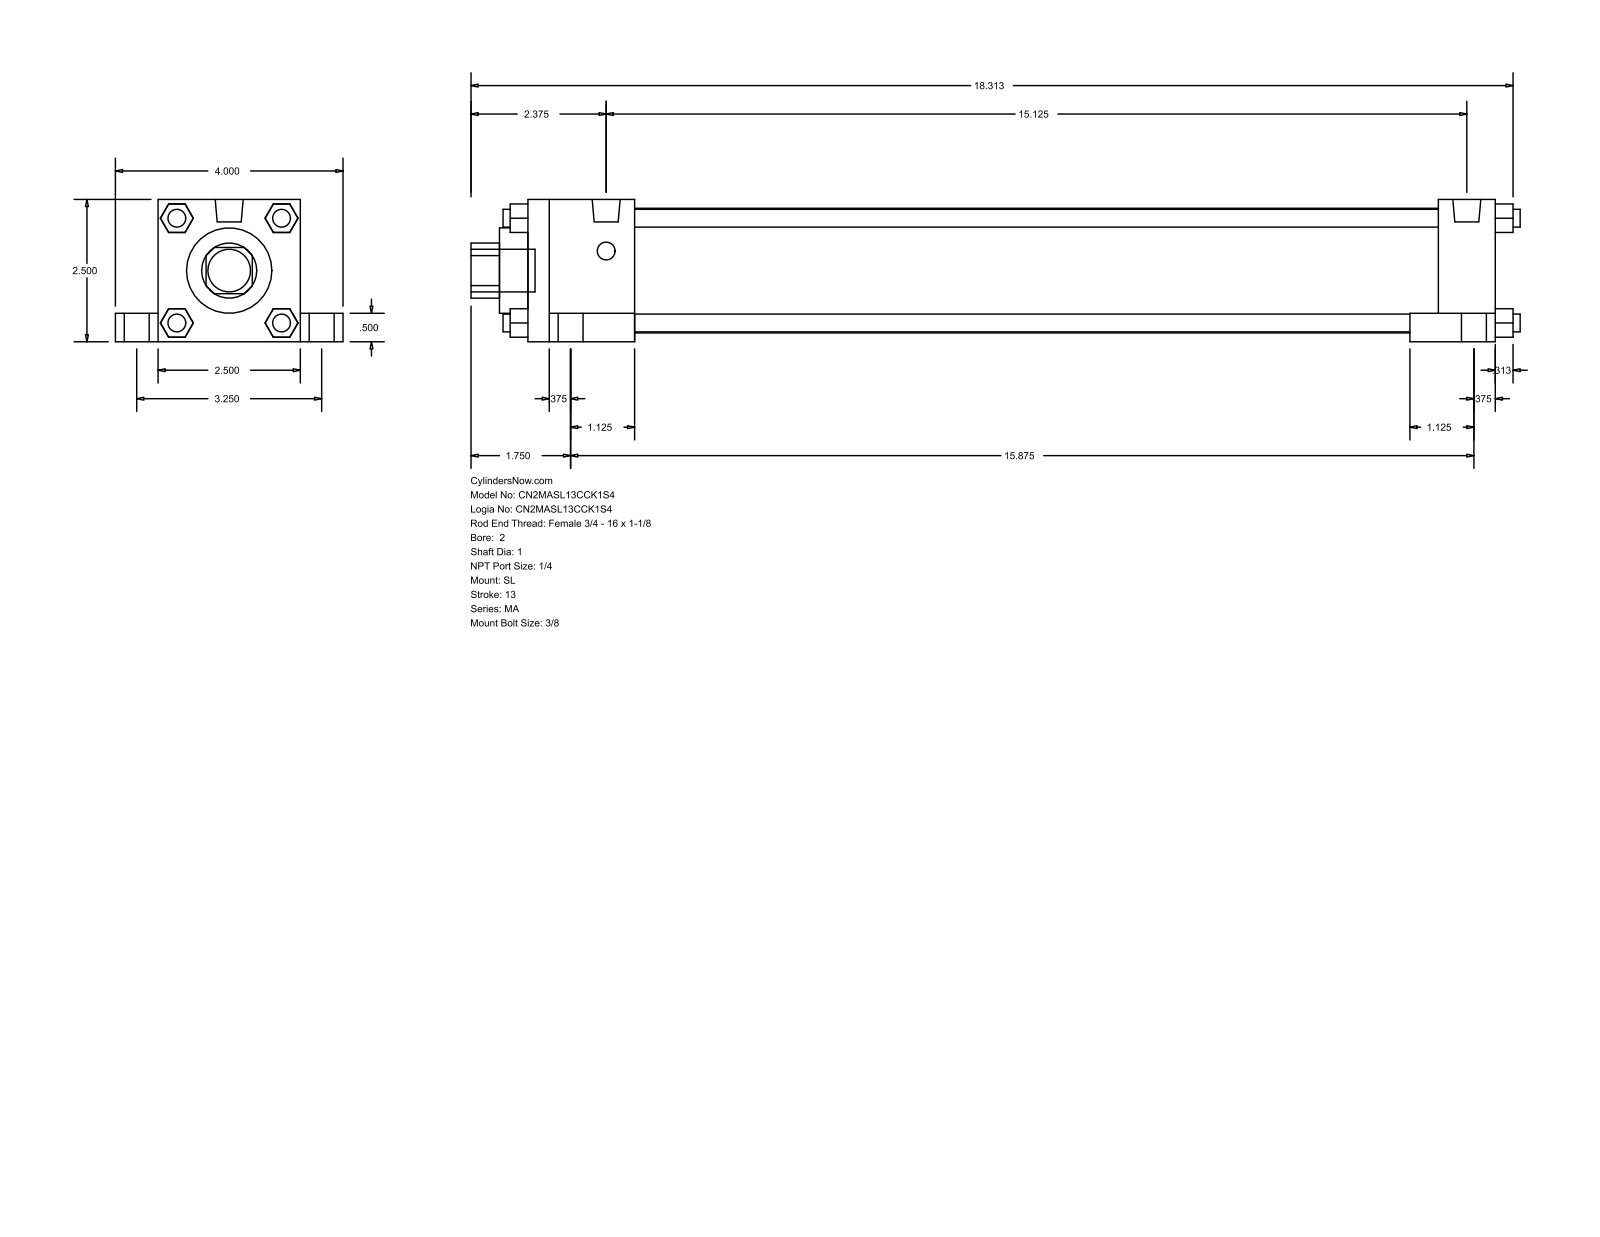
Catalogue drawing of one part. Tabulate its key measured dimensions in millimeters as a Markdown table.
| quantity | value |
| --- | --- |
| part name | MA_SL__0200_1 |
| STEP written by | GSSL Pune (CONFIG_CONTROL_DESIGN) |
| units | millimeters |
| bodies | 0 solids, 148 faces (112 planar, 36 cylindrical, 0 other) |
| overall size | 468.31 × 101.6 × 63.5 |
| round holes (diameter × count) | 25.4 × 1, 38.1 × 1, 55.63 × 1 |
| round bosses / shafts (diameter × count) | 7.94 × 8, 17.46 × 4, 11.11 × 4, 12.49 × 2, 19.05 × 1 |
| partial cylindrical surfaces (radius × count) | 12.29 × 1 |
| main face-to-face distances | 63.5, 12.7, 431.8, 19.05, 82.55, 25.4, 50.8, 47.63, 384.17, 406.4 |
